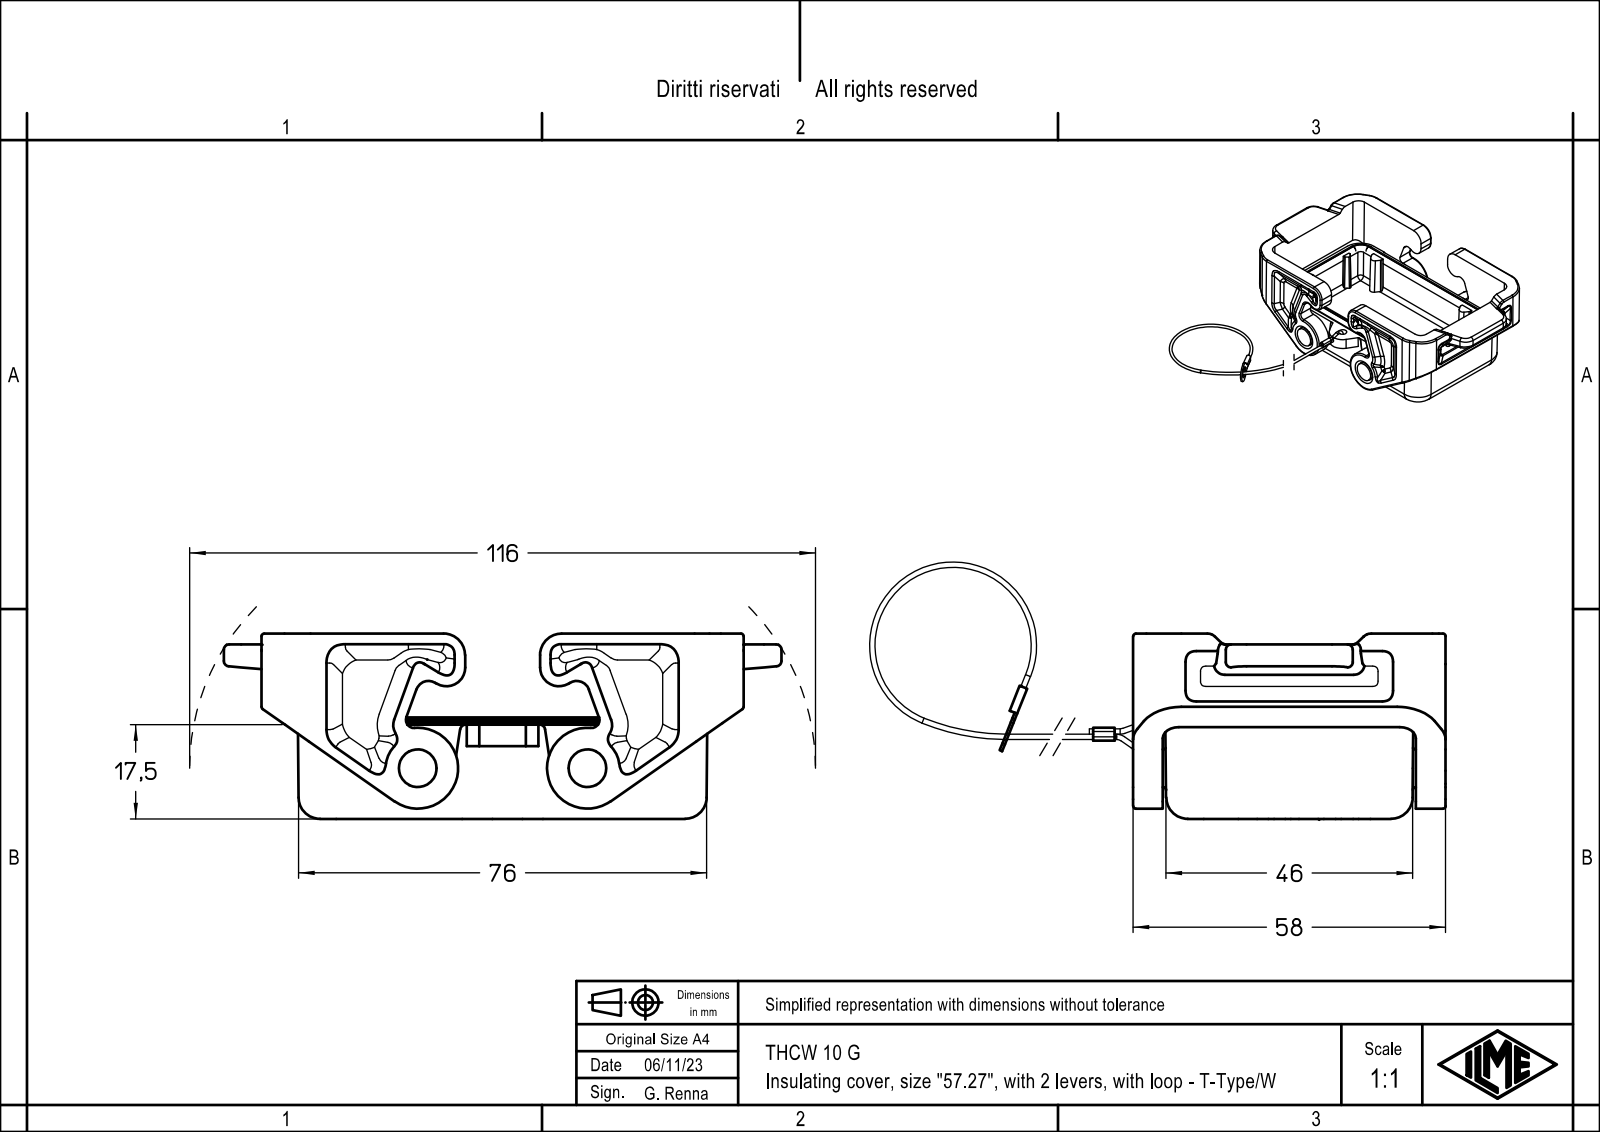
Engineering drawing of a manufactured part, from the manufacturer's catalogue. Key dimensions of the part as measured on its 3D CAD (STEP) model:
Part name (STEP PRODUCT): THCW 10 G
STEP written by: Creo Elements/Direct Modeling 20.1B 02-Apr-2019 (C) Parametric Technology GmbH (AUTOMOTIVE_DESIGN)
Units: millimetres
Bodies: 1 solid, 601 faces (214 planar, 300 cylindrical, 87 other)
Overall size (bounding box): 227.87 × 103.5 × 34.55
Volume: 58 291 mm³ · Surface area: 31 473 mm²
Round holes (diameter × count): ⌀3 ×1, ⌀4.2 ×1
Round bosses / shafts (diameter × count): ⌀1 ×5, ⌀7 ×3
Partial cylindrical surfaces — rounded edges, fillets, slot ends (radius × count): R0.15 ×44, R1 ×40, R1.5 ×18, R1.3 ×16, R3 ×16, R0.5 ×13, R2 ×12, R4 ×10
Main face-to-face distances: 5.5, 52.5, 47, 34.4, 28.9, 58, 12, 79.5, 17.5, 16.9
